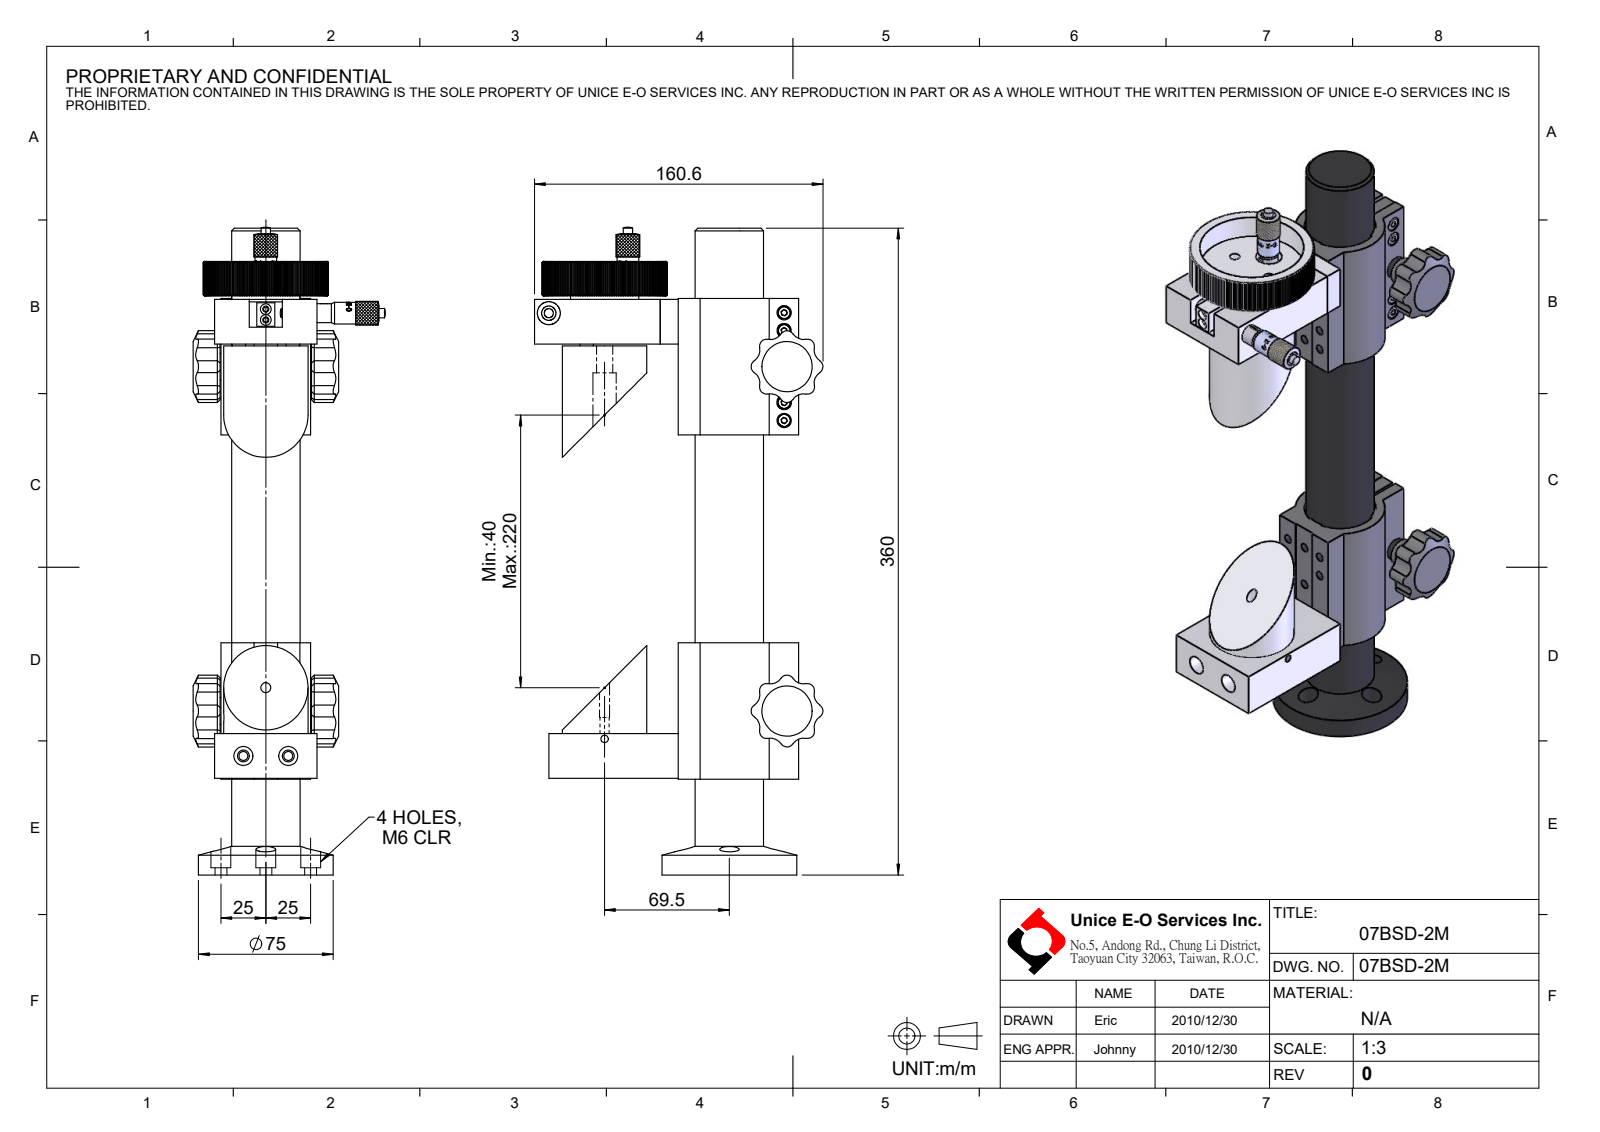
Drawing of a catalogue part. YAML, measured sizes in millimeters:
part_name: "07BSD-2M"
step_written_by: "SolidWorks 2016 (CONFIG_CONTROL_DESIGN)"
units: millimeters
bodies: {solids: 41, faces: 2814, planar: 1162, cylindrical: 712, other: 940}
overall_size: [360.46, 160.6, 107.04]
volume: 1036000
surface_area: 253302
round_holes:
  - {diameter: 5, count: 22}
  - {diameter: 3.3, count: 15}
  - {diameter: 8, count: 11}
  - {diameter: 4.5, count: 10}
  - {diameter: 6.6, count: 10}
  - {diameter: 11, count: 7}
  - {diameter: 2.5, count: 6}
  - {diameter: 10.6, count: 5}
  - {diameter: 4.2, count: 4}
  - {diameter: 6, count: 3}
  - {diameter: 3, count: 2}
  - {diameter: 3.4, count: 2}
round_bosses_or_shafts:
  - {diameter: 7, count: 8}
  - {diameter: 4, count: 8}
  - {diameter: 15, count: 2}
  - {diameter: 13, count: 2}
  - {diameter: 12.7, count: 2}
  - {diameter: 12, count: 2}
  - {diameter: 10.5, count: 2}
  - {diameter: 9.9, count: 2}
partial_cylinders:
  - {radius: 4, count: 16}
  - {radius: 7, count: 16}
  - {radius: 2, count: 2}
  - {radius: 5.98, count: 2}
  - {radius: 2.5, count: 1}
  - {radius: 20, count: 1}
  - {radius: 25, count: 1}
  - {radius: 34.75, count: 1}
face_to_face_distances: [10, 3, 6.5, 23.5, 33.5, 6, 24, 14, 30.5, 25]
hole_center_spacings: [25, 191.69, 12.5, 27.95, 50, 17.68, 26.25, 32.33]
